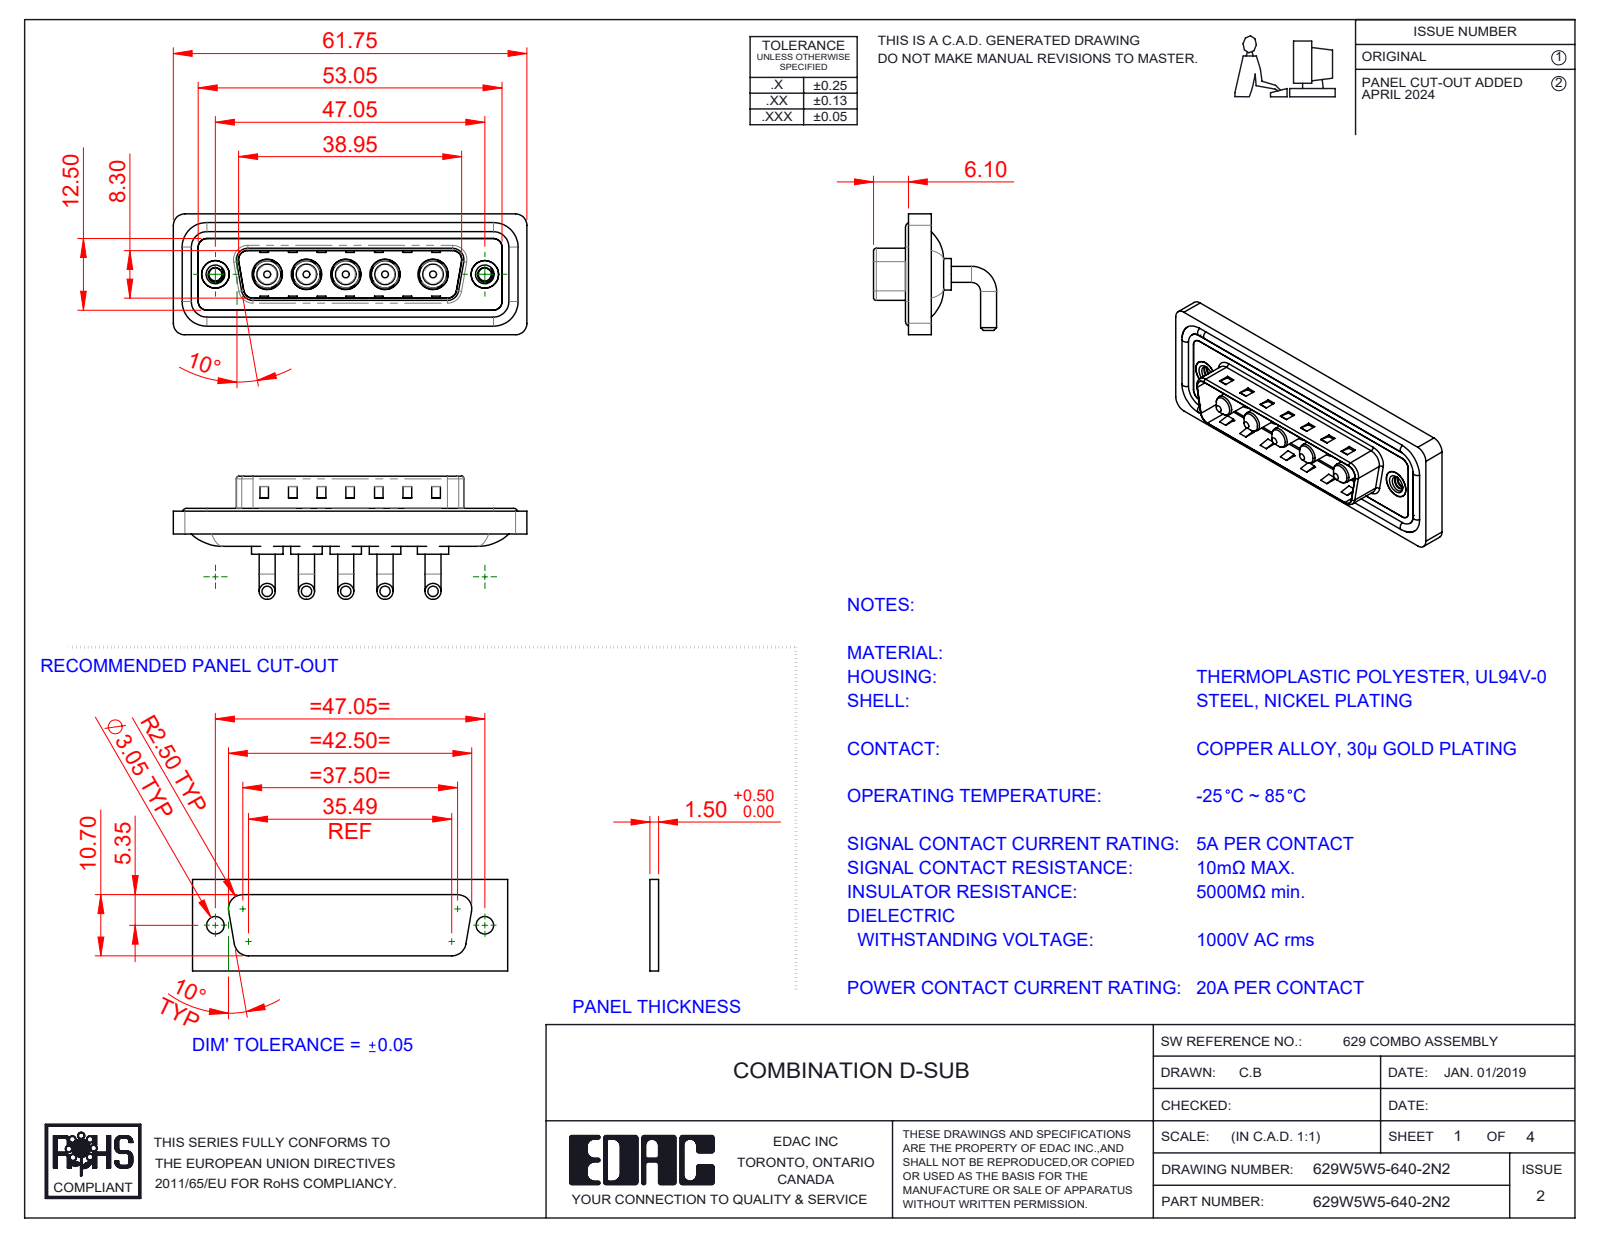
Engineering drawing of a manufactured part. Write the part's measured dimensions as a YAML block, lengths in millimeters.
part_name: "629Combo Waterproof Housing_25 Contacts; 629Combo Shell Rear_25 Contacts; 629Combo Housing_5W5; Power Pin_20A RA (+3 more)"
step_written_by: "SolidWorks 2023 (CONFIG_CONTROL_DESIGN)"
units: millimeters
bodies: {solids: 17, faces: 698, planar: 259, cylindrical: 293, other: 146}
overall_size: [61.75, 21.5, 21.1]
volume: 7813
surface_area: 12272
round_holes:
  - {diameter: 4.85, count: 5}
  - {diameter: 5.3, count: 5}
  - {diameter: 2.26, count: 2}
  - {diameter: 4, count: 2}
  - {diameter: 4.8, count: 2}
  - {diameter: 5, count: 2}
round_bosses_or_shafts:
  - {diameter: 2.8, count: 10}
  - {diameter: 5.5, count: 5}
  - {diameter: 5.2, count: 5}
  - {diameter: 4.75, count: 5}
  - {diameter: 3.75, count: 5}
  - {diameter: 3.6, count: 5}
  - {diameter: 1.6, count: 4}
  - {diameter: 4.9, count: 2}
partial_cylinders:
  - {radius: 1.5, count: 18}
  - {radius: 2, count: 18}
  - {radius: 0.5, count: 8}
  - {radius: 1.6, count: 8}
  - {radius: 2.1, count: 5}
  - {radius: 0.25, count: 4}
  - {radius: 0.6, count: 4}
  - {radius: 0.65, count: 4}
face_to_face_distances: [0.4, 2.9, 0.8, 4.5, 4.1, 1.1, 2.1, 3.1, 1.5, 6]
hole_center_spacings: [6.86, 13.73, 6.85, 6.87, 8.37, 8.38, 9.04, 9.05]
